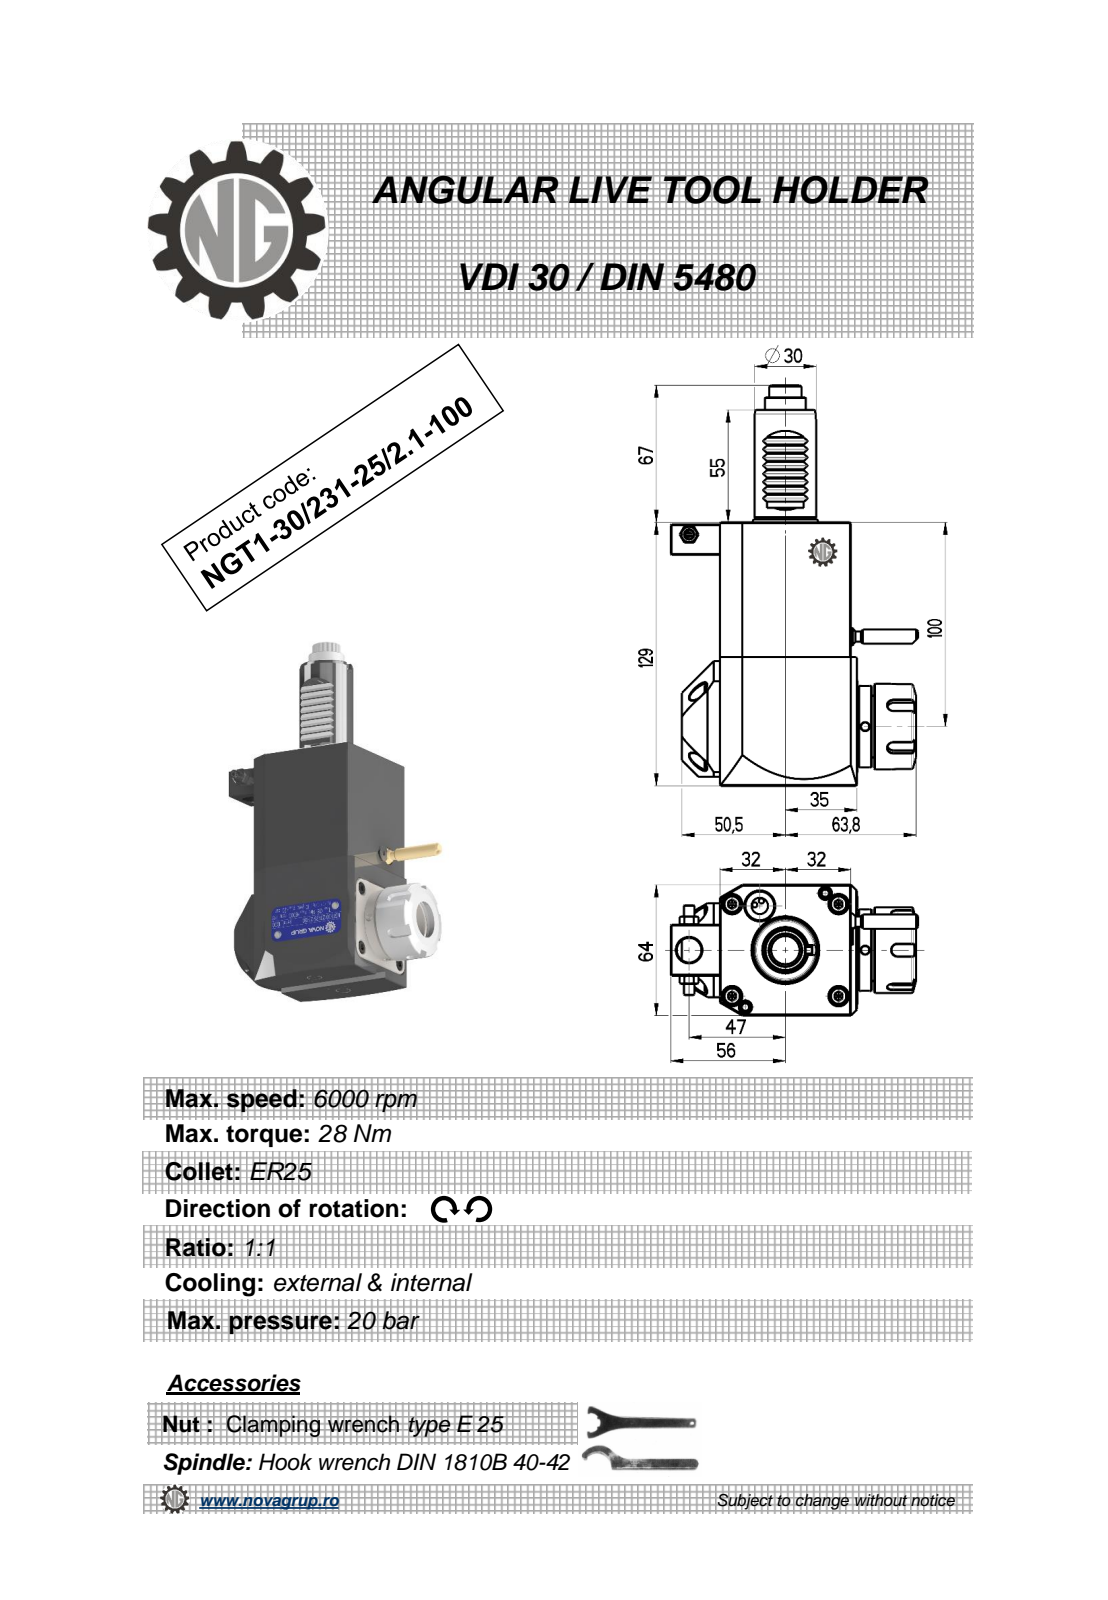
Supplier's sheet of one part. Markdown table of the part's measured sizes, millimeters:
| quantity | value |
| --- | --- |
| part name | NGT1_30_231_25_2_1_100 |
| STEP written by | PRO/ENGINEER BY PARAMETRIC TECHNOLOGY CORPORATION, 2010280 (CONFIG_CONTROL_DESIGN) |
| units | millimeters |
| bodies | 1 solid, 498 faces (184 planar, 157 cylindrical, 157 other) |
| overall size | 196 × 120.88 × 65.6 |
| volume | 643 488 mm³ |
| surface area | 58 785 mm² |
| round holes (diameter × count) | 4 × 2, 2.5 × 1, 3 × 1, 4.2 × 1, 9.5 × 1, 12 × 1, 20.3 × 1 |
| round bosses / shafts (diameter × count) | 8.96 × 2, 5 × 2, 42 × 1, 40 × 1, 33 × 1, 30 × 1, 20 × 1, 7 × 1 |
| partial cylindrical surfaces (radius × count) | 1.98 × 36, 0.26 × 12, 0.3 × 8, 3 × 5, 160 × 2, 7.08 × 1, 7.92 × 1, 13 × 1 |
| main face-to-face distances | 64, 129, 67.2, 3.2, 67, 3, 18.5, 0.5, 82.5, 85.5 |
| hole center spacings | 46.17, 49.52, 85.95, 91.5, 127.37 |
